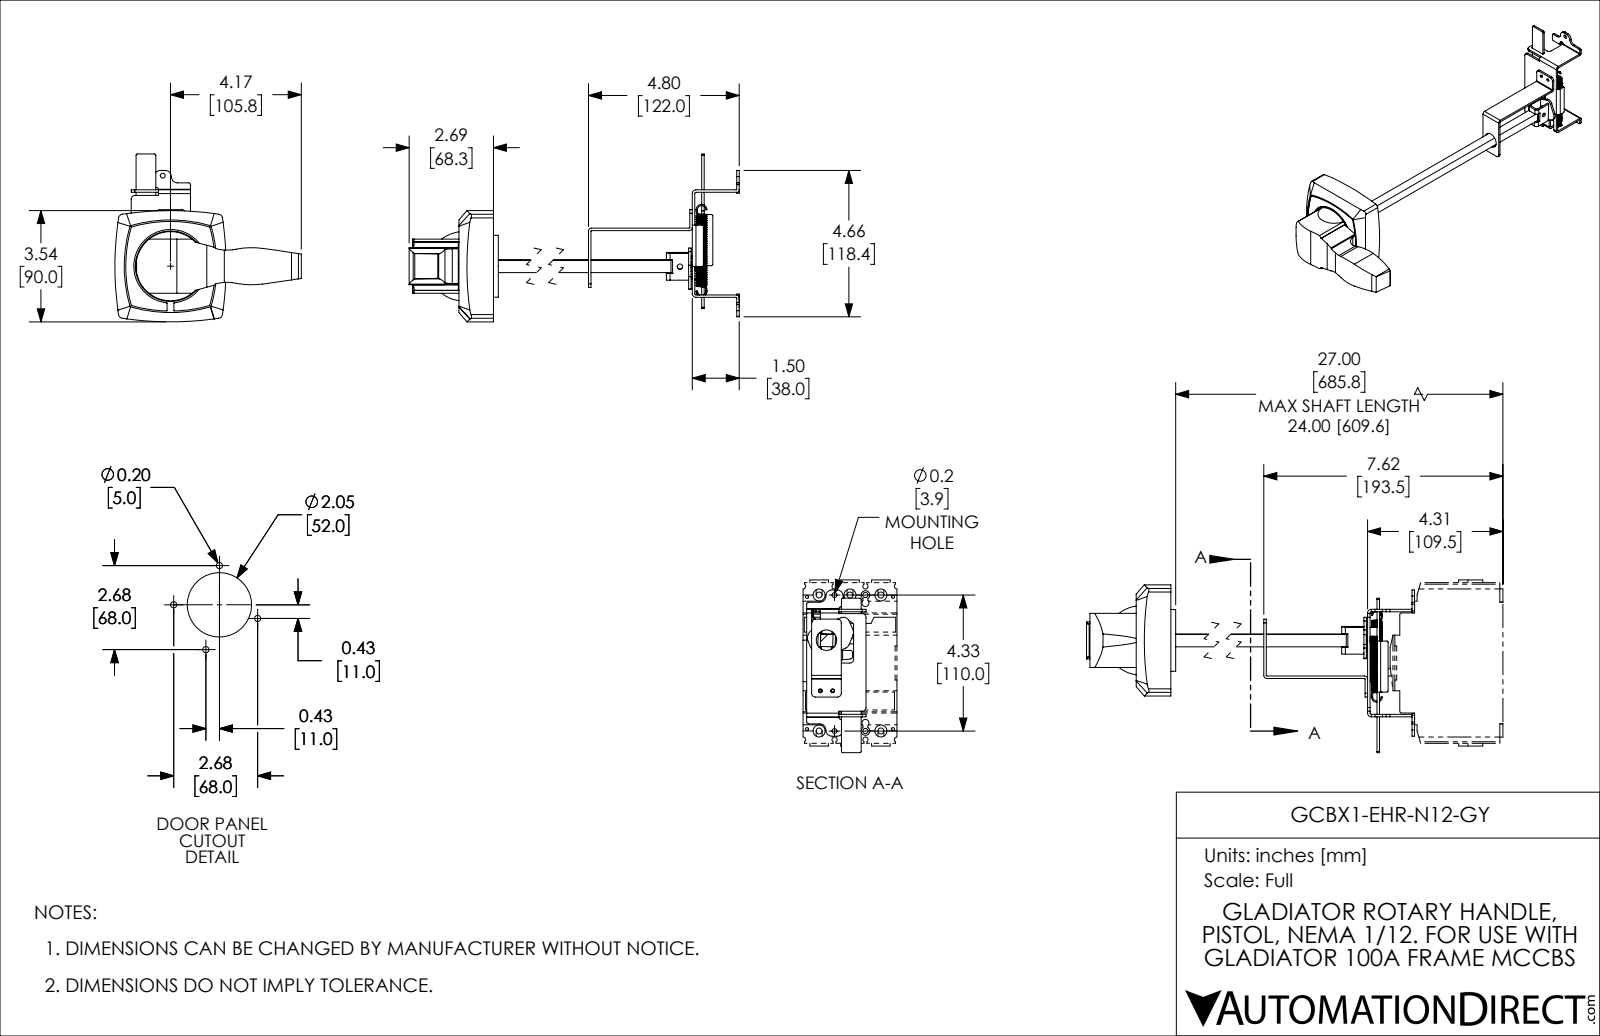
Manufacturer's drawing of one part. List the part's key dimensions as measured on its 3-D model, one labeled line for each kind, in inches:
Part name (STEP PRODUCT): GCBX1-EHR-N12-GY
STEP written by: SolidWorks 2021 (CONFIG_CONTROL_DESIGN)
Units: inches
Bodies: 6 solids, 577 faces (235 planar, 242 cylindrical, 100 other)
Overall size (bounding box): 15.94 × 5.939 × 5.346
Volume: 23.6 in³ · Surface area: 148.3 in²
Round holes (diameter × count): ⌀0.197 ×4, ⌀0.118 ×3, ⌀0.106 ×2, ⌀0.122 ×2, ⌀0.154 ×2, ⌀0.098 ×1, ⌀0.161 ×1, ⌀0.169 ×1, ⌀0.327 ×1, ⌀0.65 ×1, ⌀1.969 ×1, ⌀2.244 ×1
Round bosses / shafts (diameter × count): ⌀0.098 ×3, ⌀2.343 ×1, ⌀1.969 ×1, ⌀0.354 ×1, ⌀0.315 ×1, ⌀0.276 ×1, ⌀0.236 ×1, ⌀0.157 ×1
Partial cylindrical surfaces — rounded edges, fillets, slot ends (radius × count): R0.118 ×29, R0.039 ×23, R0.02 ×21, R0.012 ×12, R0.059 ×12, R0.008 ×10, R0.197 ×8, R0.079 ×6
Main face-to-face distances: 0.079, 0.299, 11.897, 13.019, 0.394, 0.394, 12.799, 0.157, 11.819, 13.098
Hole centre spacings: 0.341, 0.585, 1.339, 1.407, 1.626, 2.712, 0.213, 0.328
